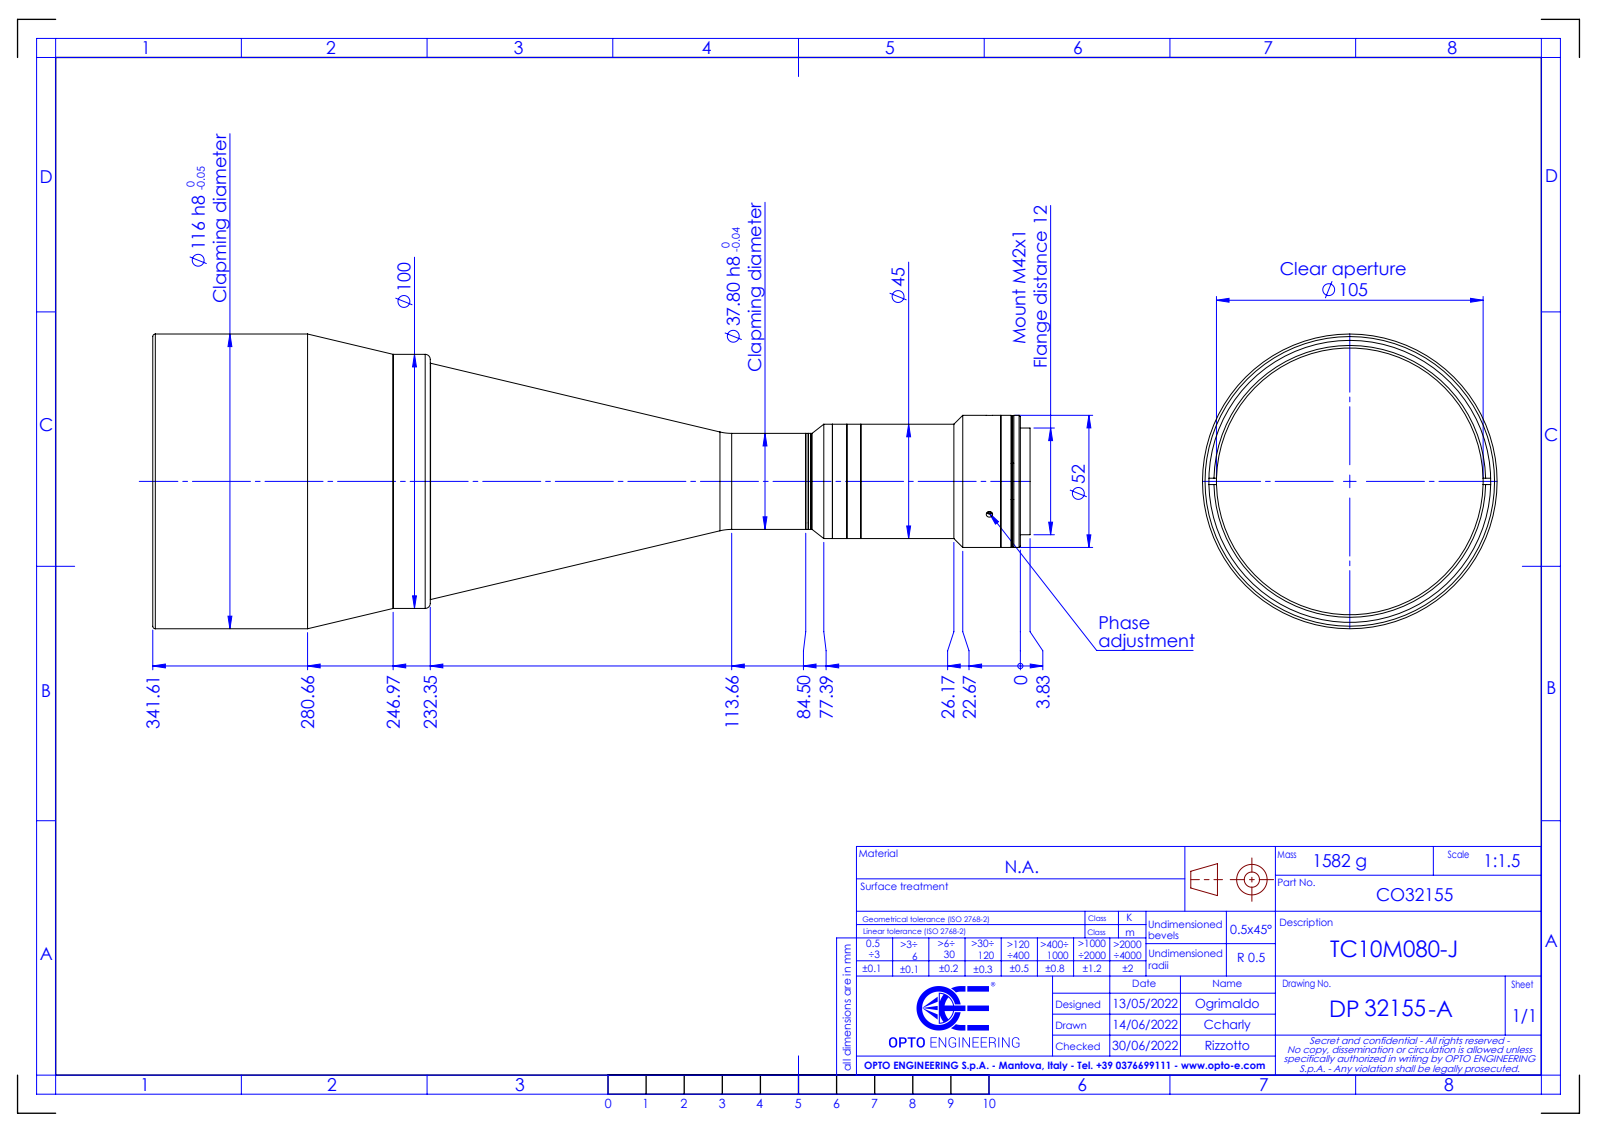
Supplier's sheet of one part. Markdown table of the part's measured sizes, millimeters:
| quantity | value |
| --- | --- |
| part name | DP32155-A_TC10M080-J |
| STEP written by | SolidWorks 2021 (CONFIG_CONTROL_DESIGN) |
| units | millimeters |
| bodies | 0 solids, 97 faces (21 planar, 52 cylindrical, 24 other) |
| overall size | 345.43 × 116 × 116 |
| round holes (diameter × count) | 2.5 × 3, 38 × 1, 41 × 1, 105 × 1, 111 × 1 |
| round bosses / shafts (diameter × count) | 116 × 1, 100 × 1, 93 × 1, 52 × 1, 51.8 × 1, 45 × 1, 42 × 1, 37.8 × 1 |
| main face-to-face distances | 94.1, 338.51, 244.41, 337.39, 243.29, 1.12, 341.07, 246.97, 3.68, 2.56 |
